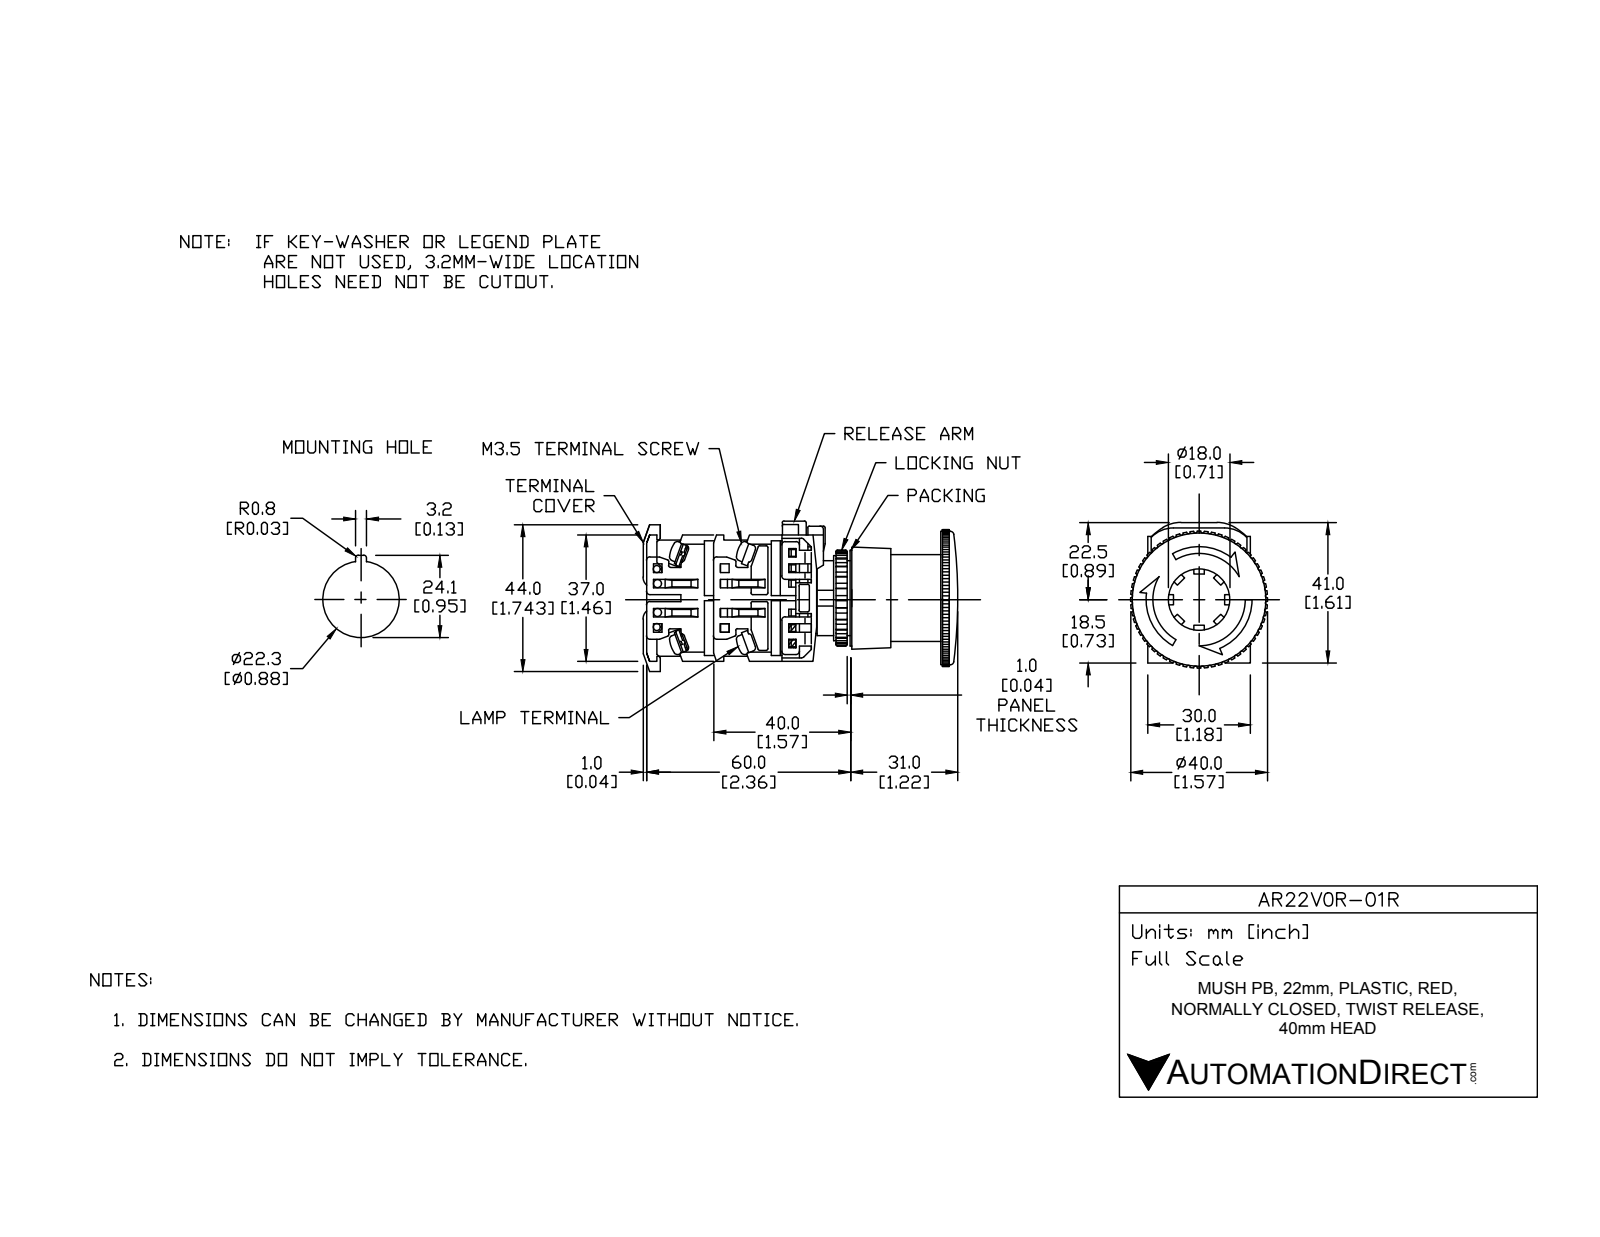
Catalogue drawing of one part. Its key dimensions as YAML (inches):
part_name: "AR22V0R-01R"
step_written_by: "SolidWorks 2017 (AUTOMOTIVE_DESIGN)"
units: inches
bodies: {solids: 11, faces: 585, planar: 212, cylindrical: 273, other: 100}
overall_size: [2.854, 1.693, 1.574]
volume: 2.241
surface_area: 33.66
round_holes:
  - {diameter: 0.858, count: 1}
  - {diameter: 0.866, count: 1}
  - {diameter: 1, count: 1}
round_bosses_or_shafts:
  - {diameter: 0.197, count: 2}
  - {diameter: 1.173, count: 1}
  - {diameter: 0.984, count: 1}
  - {diameter: 0.945, count: 1}
  - {diameter: 0.856, count: 1}
  - {diameter: 0.669, count: 1}
partial_cylinders:
  - {radius: 0.02, count: 103}
  - {radius: 0.069, count: 4}
  - {radius: 0.197, count: 4}
  - {radius: 0.157, count: 2}
  - {radius: 0.531, count: 1}
  - {radius: 0.591, count: 1}
  - {radius: 0.653, count: 1}
  - {radius: 0.693, count: 1}
face_to_face_distances: [0.039, 1.142, 0.394, 0.079, 0.709, 0.807, 0.886, 0.63, 0.492, 1.831]
